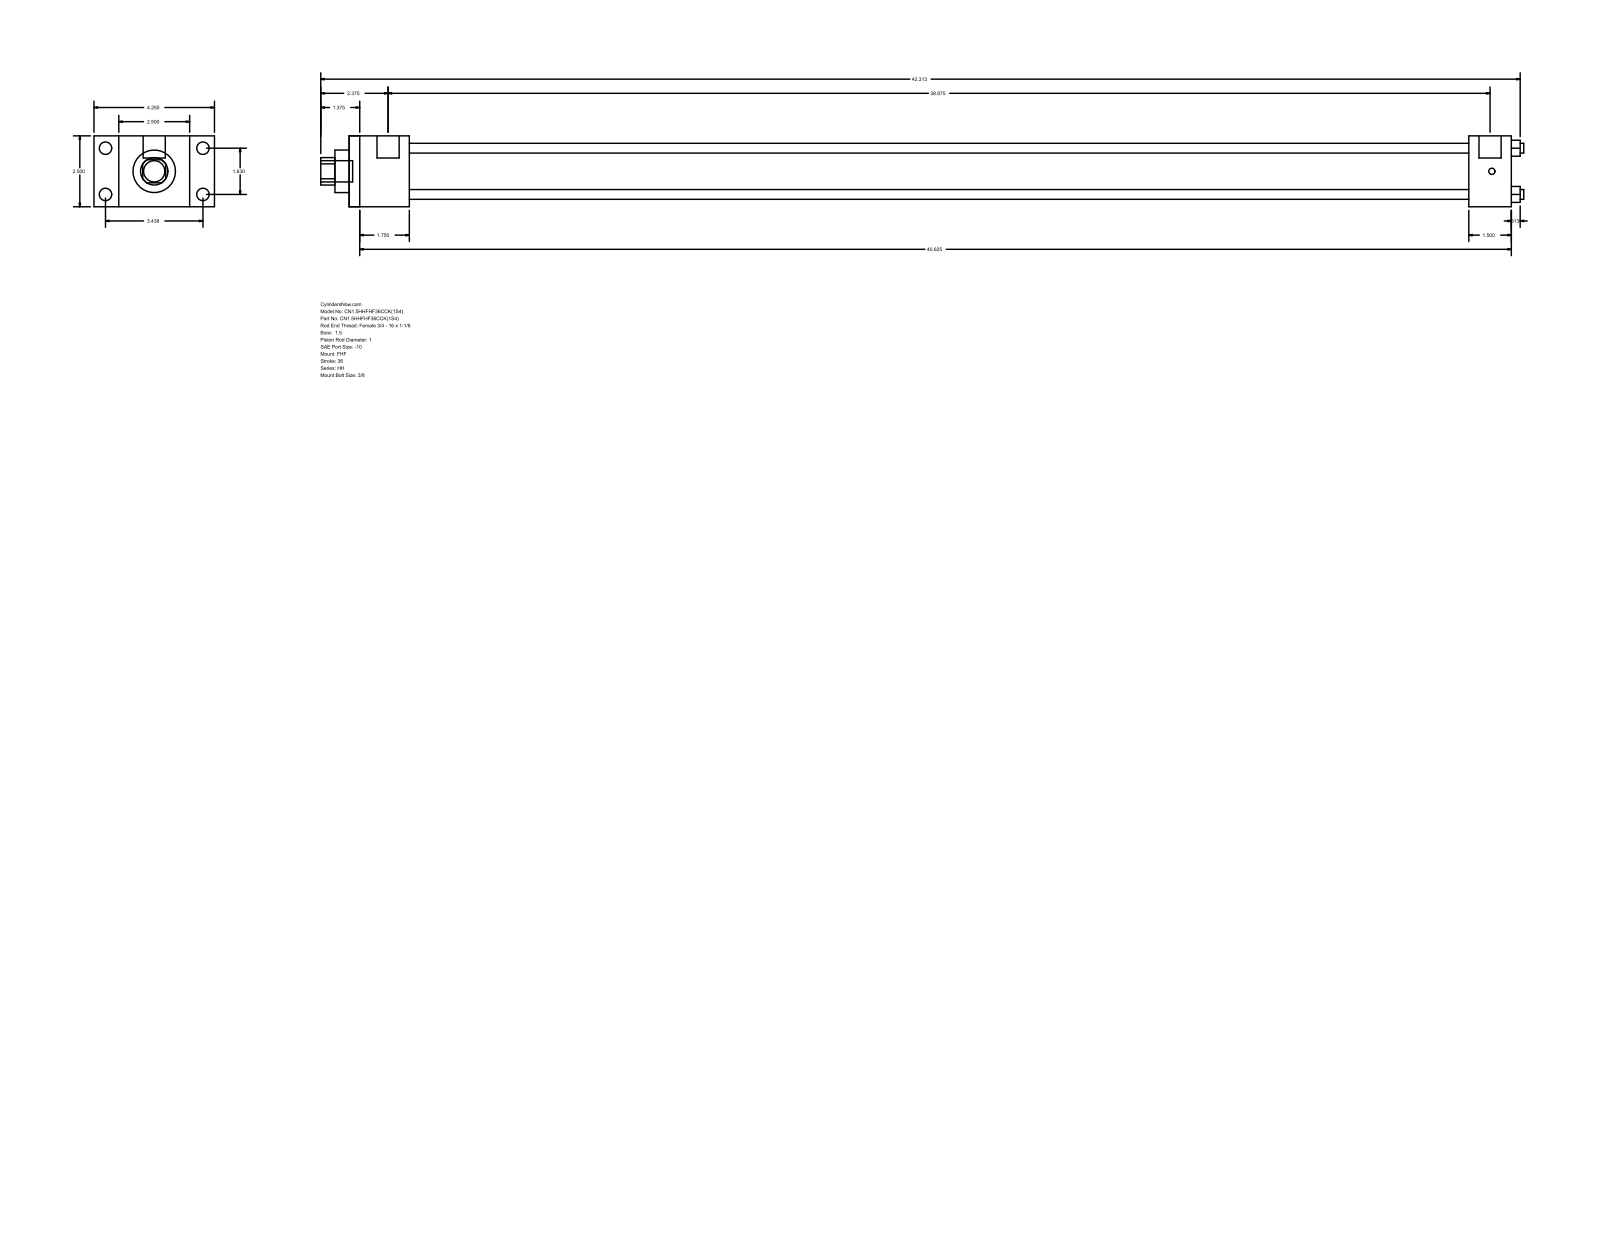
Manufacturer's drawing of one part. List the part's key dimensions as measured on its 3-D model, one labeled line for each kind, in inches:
Part name (STEP PRODUCT): HH_FHF__0150_1
STEP written by: GSSL Pune (CONFIG_CONTROL_DESIGN)
Units: inches
Bodies: 0 solids, 88 faces (60 planar, 28 cylindrical, 0 other)
Overall size (bounding box): 42.437 × 4.25 × 2.5
Round holes (diameter × count): ⌀0.345 ×4, ⌀1 ×1, ⌀1.5 ×1, ⌀1.75 ×1
Round bosses / shafts (diameter × count): ⌀0.438 ×4, ⌀0.219 ×4, ⌀0.781 ×2, ⌀0.75 ×1
Partial cylindrical surfaces — rounded edges, fillets, slot ends (radius × count): R0.484 ×1
Main face-to-face distances: 2.5, 0.875, 3.375, 2.125, 4.25, 41, 38.875, 39.5, 37.375, 1.5
Hole centre spacings: 1.152, 1.63, 2.305
